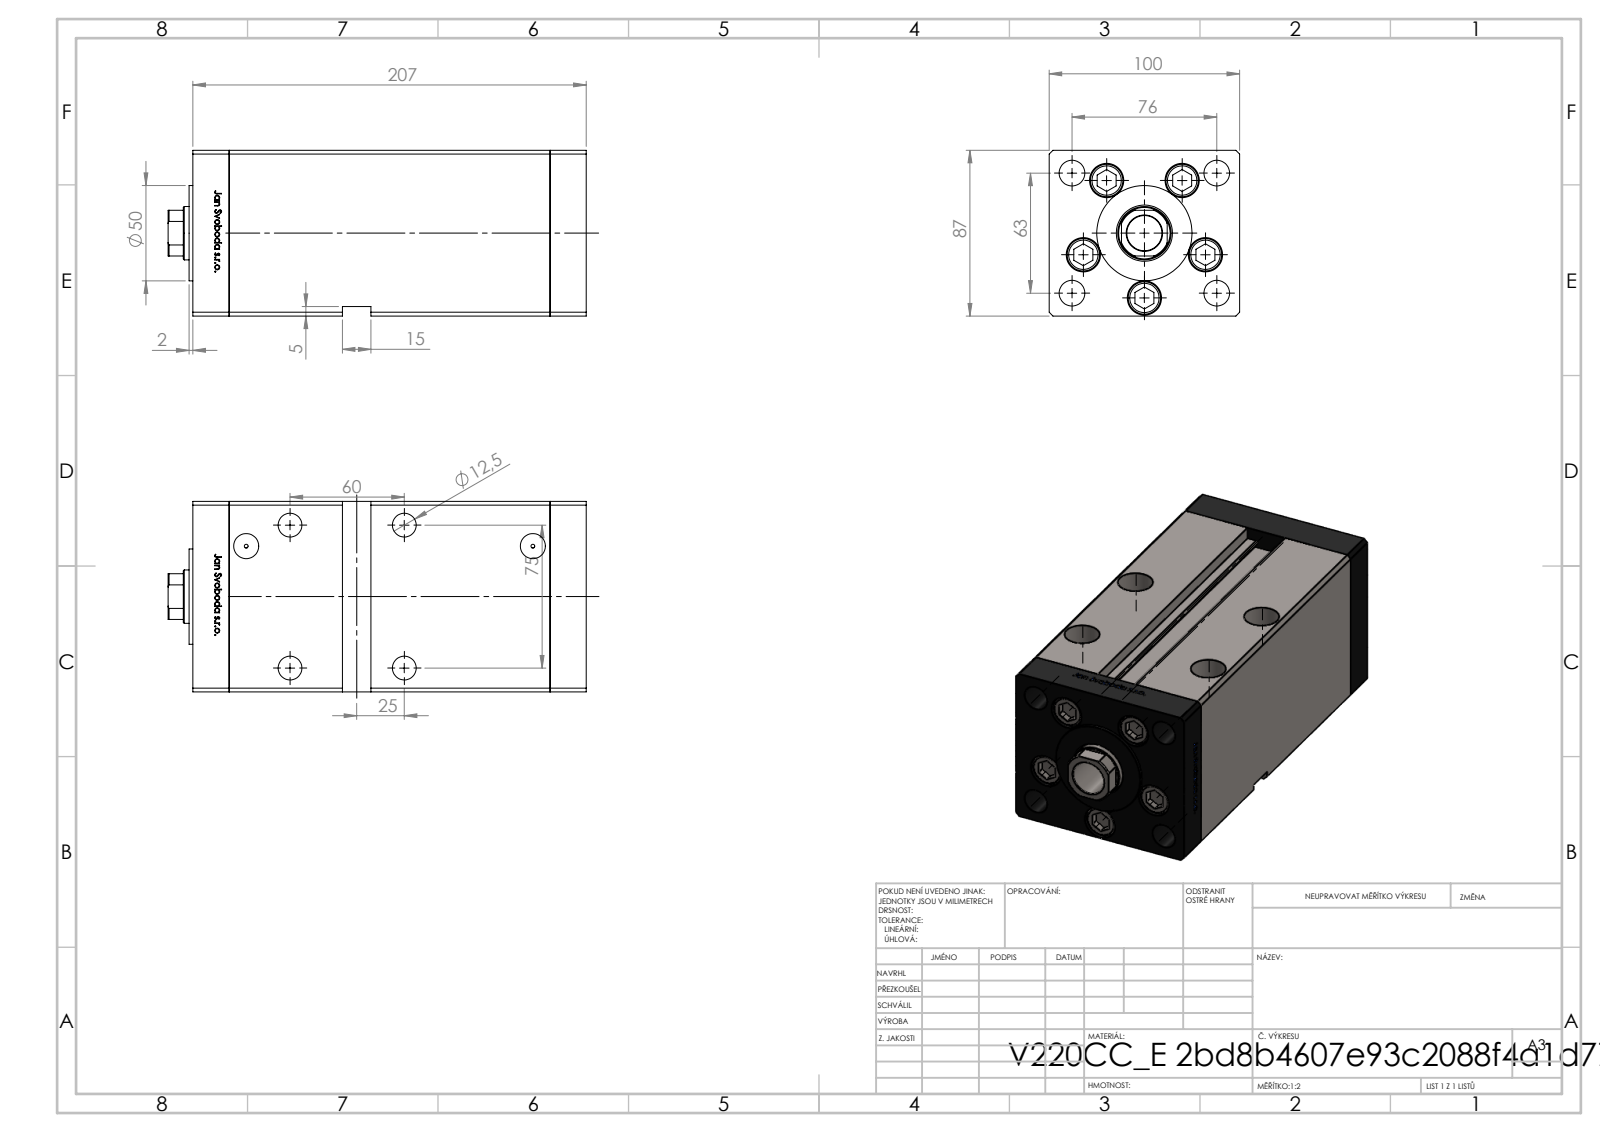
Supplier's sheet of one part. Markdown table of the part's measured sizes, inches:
| quantity | value |
| --- | --- |
| part name | V220C_E MIDDLE; V220C_VC_E; ALLEN BOLT; V220C BACK_E (+1 more) |
| STEP written by | SolidWorks 2019 (CONFIG_CONTROL_DESIGN) |
| units | inches |
| bodies | 14 solids, 1214 faces (475 planar, 165 cylindrical, 574 other) |
| overall size | 8.642 × 3.937 × 3.425 |
| volume | 92.02 in³ |
| surface area | 362.4 in² |
| round holes (diameter × count) | 0.531 × 11, 0.709 × 5, 0.728 × 5, 0.492 × 4, 0.079 × 2, 0.518 × 2, 1.102 × 1, 1.161 × 1 |
| round bosses / shafts (diameter × count) | 0.669 × 5, 0.315 × 5, 1.969 × 1 |
| partial cylindrical surfaces (radius × count) | 0.037 × 2, 0.531 × 1 |
| main face-to-face distances | 3.937, 3.425, 0.748, 6.634, 7.382, 1.348, 8.13, 0.6, 6.033, 6.781 |
| hole center spacings | 1.339, 0.732, 1.561, 1.943, 2.281, 0.828, 1.499, 1.546 |
